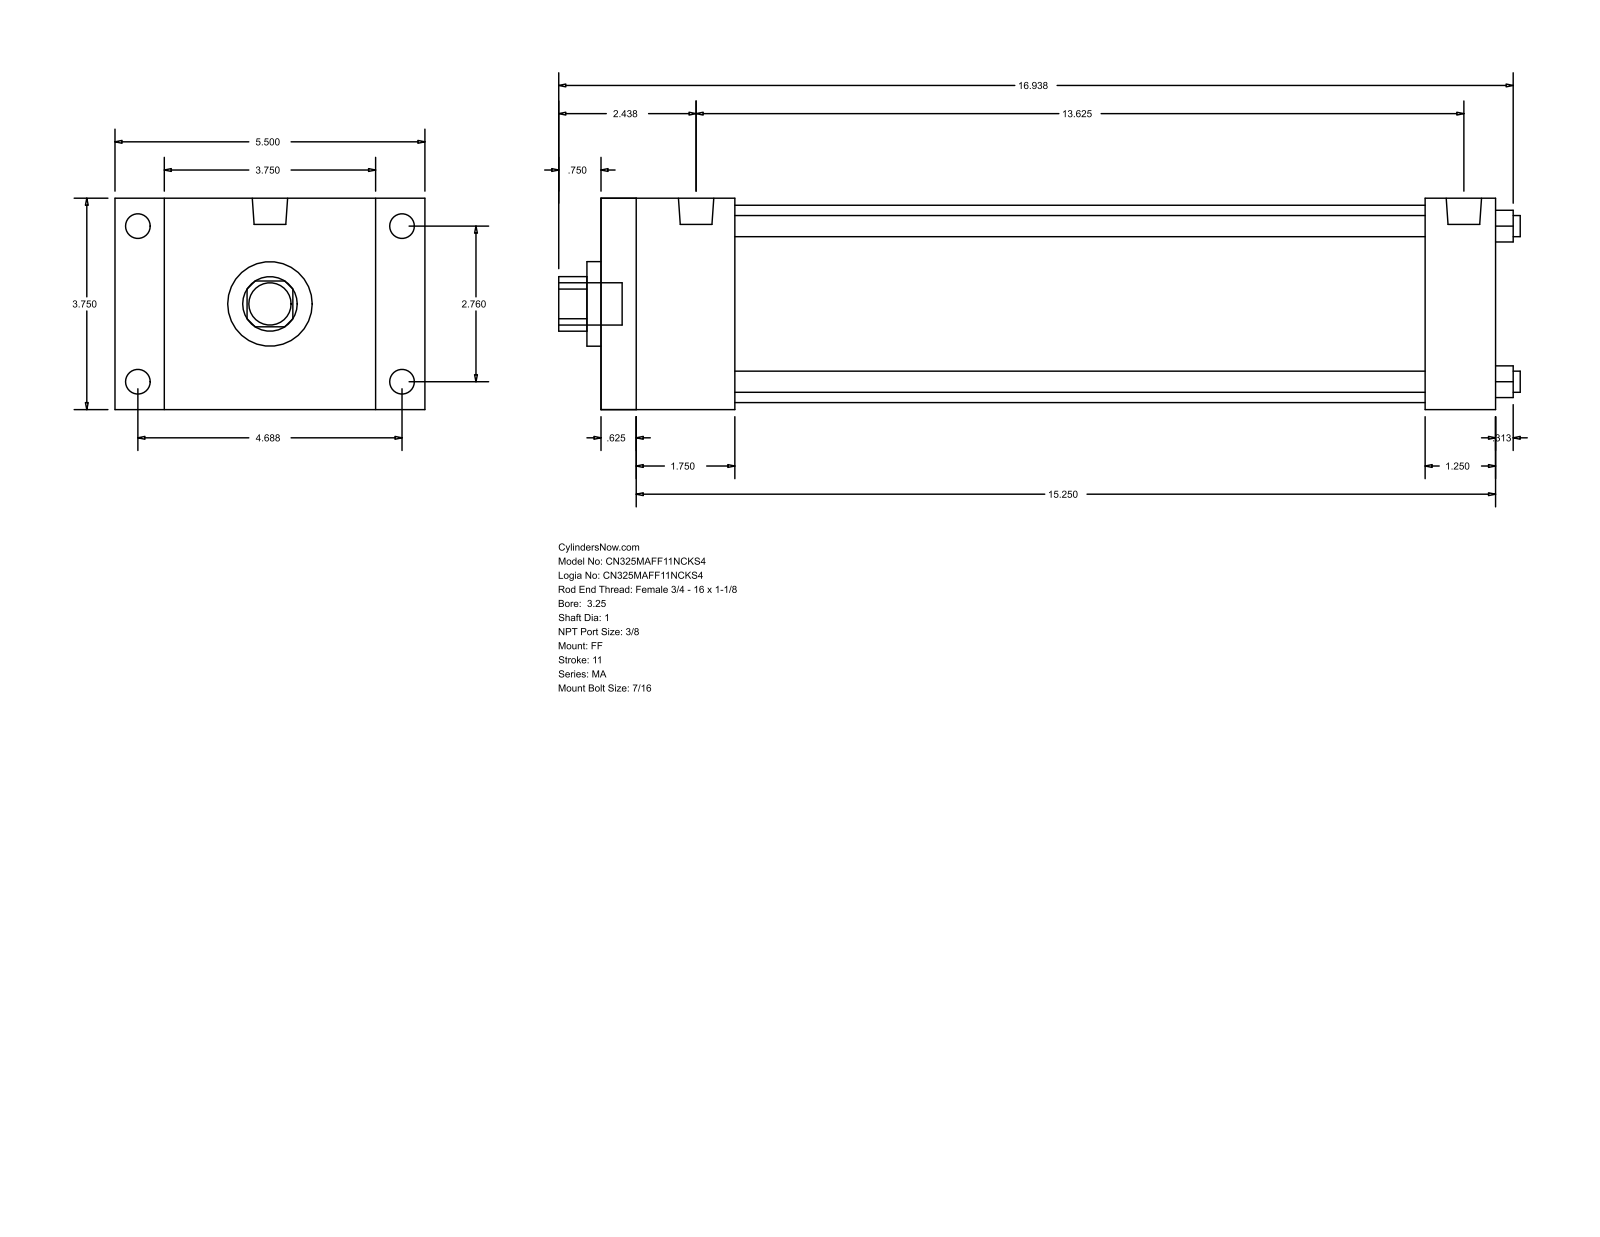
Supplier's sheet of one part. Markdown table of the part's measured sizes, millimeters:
| quantity | value |
| --- | --- |
| part name | MA_FF__0325_1 |
| STEP written by | GSSL Pune (CONFIG_CONTROL_DESIGN) |
| units | millimeters |
| bodies | 0 solids, 92 faces (64 planar, 28 cylindrical, 0 other) |
| overall size | 433.39 × 139.7 × 95.25 |
| round holes (diameter × count) | 9.53 × 4, 25.4 × 1, 38.1 × 1, 88.9 × 1 |
| round bosses / shafts (diameter × count) | 11.11 × 8, 15.93 × 2, 19.05 × 1 |
| partial cylindrical surfaces (radius × count) | 12.29 × 1 |
| main face-to-face distances | 95.24, 403.22, 15.87, 387.35, 22.23, 117.47, 60.33, 371.47, 44.46, 355.6 |
| hole center spacings | 49.57, 70.1, 99.14 |
